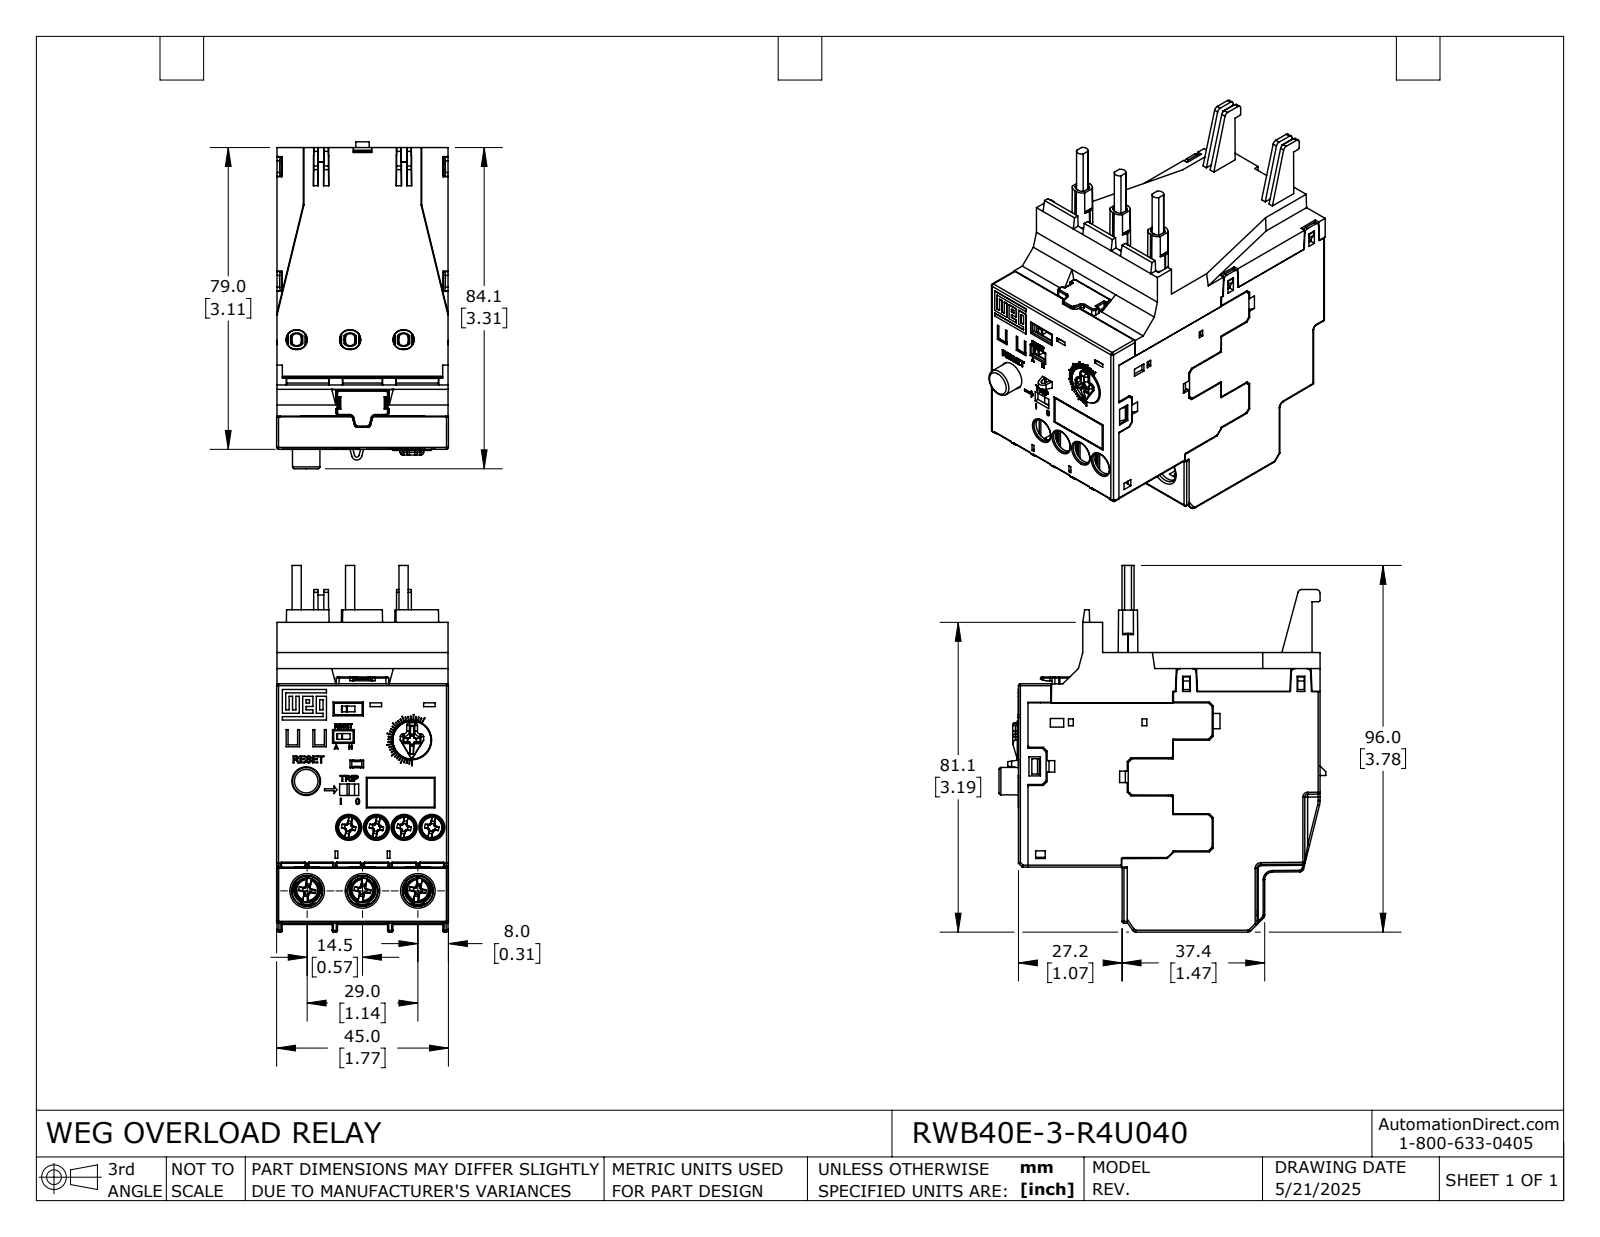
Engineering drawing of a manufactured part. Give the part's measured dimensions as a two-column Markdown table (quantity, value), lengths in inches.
| quantity | value |
| --- | --- |
| part name | RWB40E-3-R4U040 |
| STEP written by | SolidWorks 2024 (AUTOMOTIVE_DESIGN) |
| units | inches |
| bodies | 38 solids, 3774 faces (2406 planar, 808 cylindrical, 560 other) |
| overall size | 3.78 × 3.37 × 1.772 |
| volume | 10.1 in³ |
| surface area | 114.7 in² |
| round holes (diameter × count) | 0.118 × 9, 0.102 × 6, 0.098 × 4, 0.114 × 3, 0.173 × 3, 0.295 × 1, 0.406 × 1 |
| round bosses / shafts (diameter × count) | 0.138 × 7, 0.087 × 4, 0.295 × 3, 0.165 × 3, 0.114 × 3, 0.098 × 3 |
| partial cylindrical surfaces (radius × count) | 0.012 × 216, 0.02 × 76, 0.039 × 55, 0.008 × 43, 0.01 × 17, 0.037 × 17, 0.016 × 16, 0.059 × 14 |
| main face-to-face distances | 1.764, 0.286, 0.572, 0.049, 0.039, 0.244, 0.857, 0.402, 0.042, 0.53 |
| hole center spacings | 0.286, 0.572, 0.663, 0.857, 0.551, 0.571, 0.662, 0.776 |
